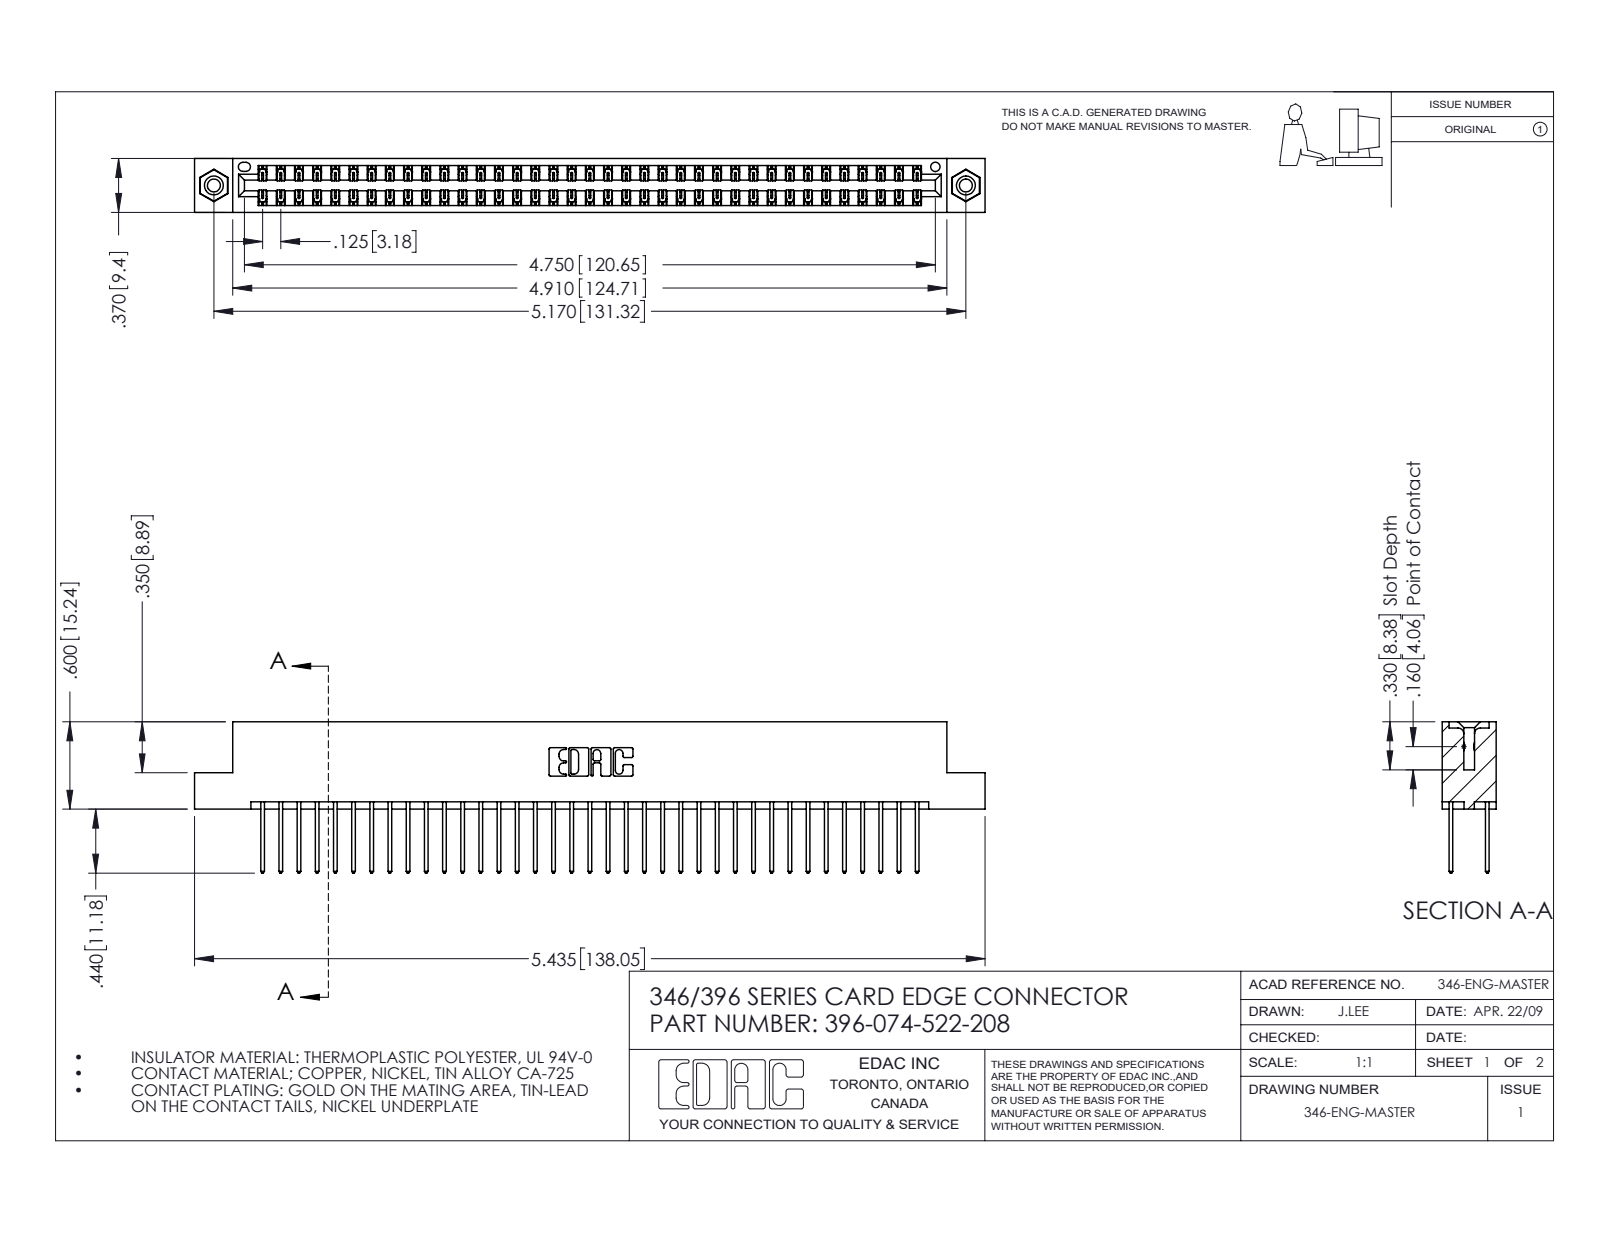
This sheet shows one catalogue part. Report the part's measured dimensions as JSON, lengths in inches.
{"part_name": "346 Part_Flush Mounting Lugs - 0.156 Dia-TI; 345-292-001_345-293-122; 345-250-001_345-250-003-102; 396-074-522-208", "step_written_by": "SolidWorks 2016 (CONFIG_CONTROL_DESIGN)", "units": "inches", "bodies": {"solids": 77, "faces": 4030, "planar": 2698, "cylindrical": 1316, "other": 16}, "overall_size": [5.435, 1.04, 0.37], "volume_in3": 0.83, "surface_area_in2": 30.26, "round_holes": [[0.089, 2], [0.125, 2], [0.156, 2], [0.064, 1]], "round_bosses_or_shafts": [[0.155, 2]], "partial_cylinders_radius": [[0.006, 111], [0.01, 74], [0.01, 22], [0.007, 6], [0.031, 6], [0.026, 3], [0.014, 2], [0.022, 2]], "face_to_face_distances": [0.048, 0.322, 0.25, 0.37, 0.072, 0.298, 0.025, 0.275, 0.148, 0.222], "hole_center_spacings": [0.246, 4.961, 5.17]}
